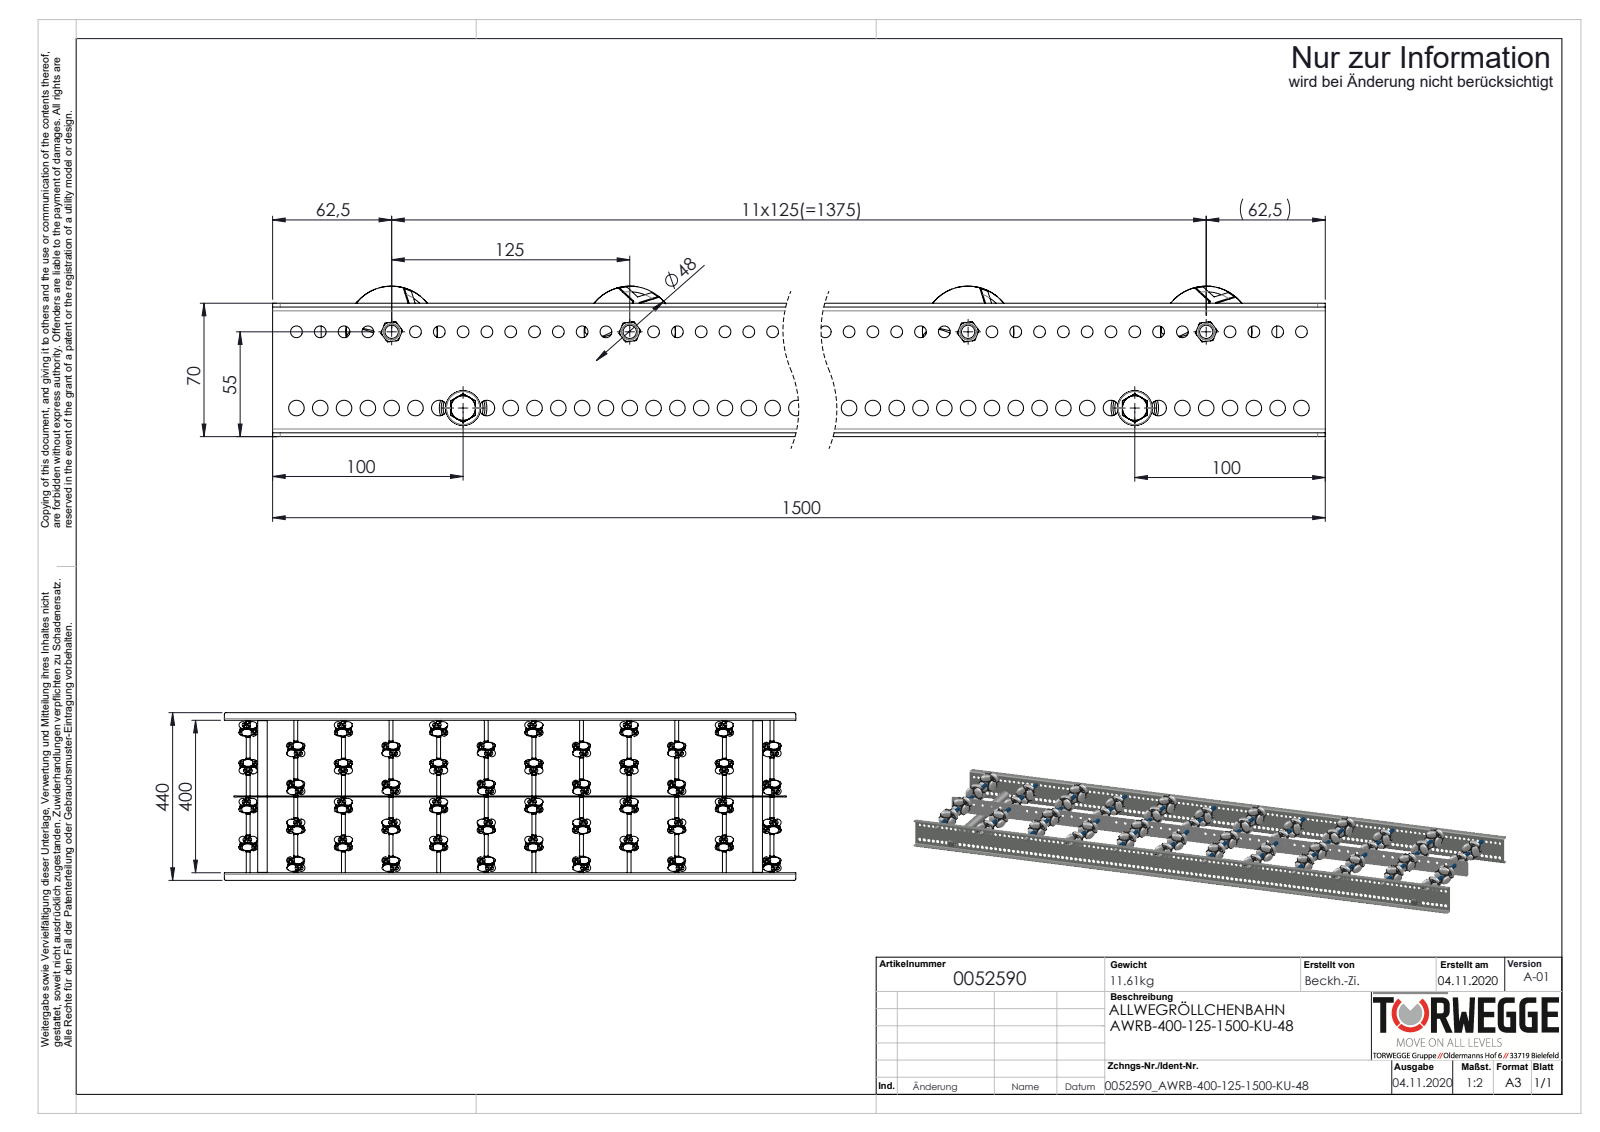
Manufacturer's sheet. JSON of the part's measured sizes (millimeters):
{"part_name": "AWR-Achse-für-Konfiguration_L400; AWR48_Röllchen; S108767_Längstraverse-42x2,5-AWR_L1449; 0019719_Gewindestange-M6_L=420 (+8 more)", "step_written_by": "SolidWorks 2020 (AUTOMOTIVE_DESIGN)", "units": "millimeters", "bodies": {"solids": 817, "faces": 15206, "planar": 5046, "cylindrical": 6240, "other": 3920}, "overall_size": [1500, 440, 79], "volume_mm3": 3181000, "surface_area_mm2": 2327000, "round_holes": [[3.7, 288], [4.2, 288], [6.2, 119], [8.2, 119], [6.5, 58], [4.92, 12], [8.4, 12], [6.8, 2], [21, 2]], "round_bosses_or_shafts": [[4, 288], [3.7, 253], [8, 14], [42, 12], [11, 12], [10, 12], [7, 12], [6, 12]], "partial_cylinders_radius": [[23.55, 12], [4, 8], [2, 4], [5, 4]], "face_to_face_distances": [2, 402, 68, 400, 404, 200.6, 198.6, 201.4, 203.4, 203.1], "hole_center_spacings": [36.06, 36.05, 10, 36.04, 55.27, 36.07, 12.5, 239.64]}
